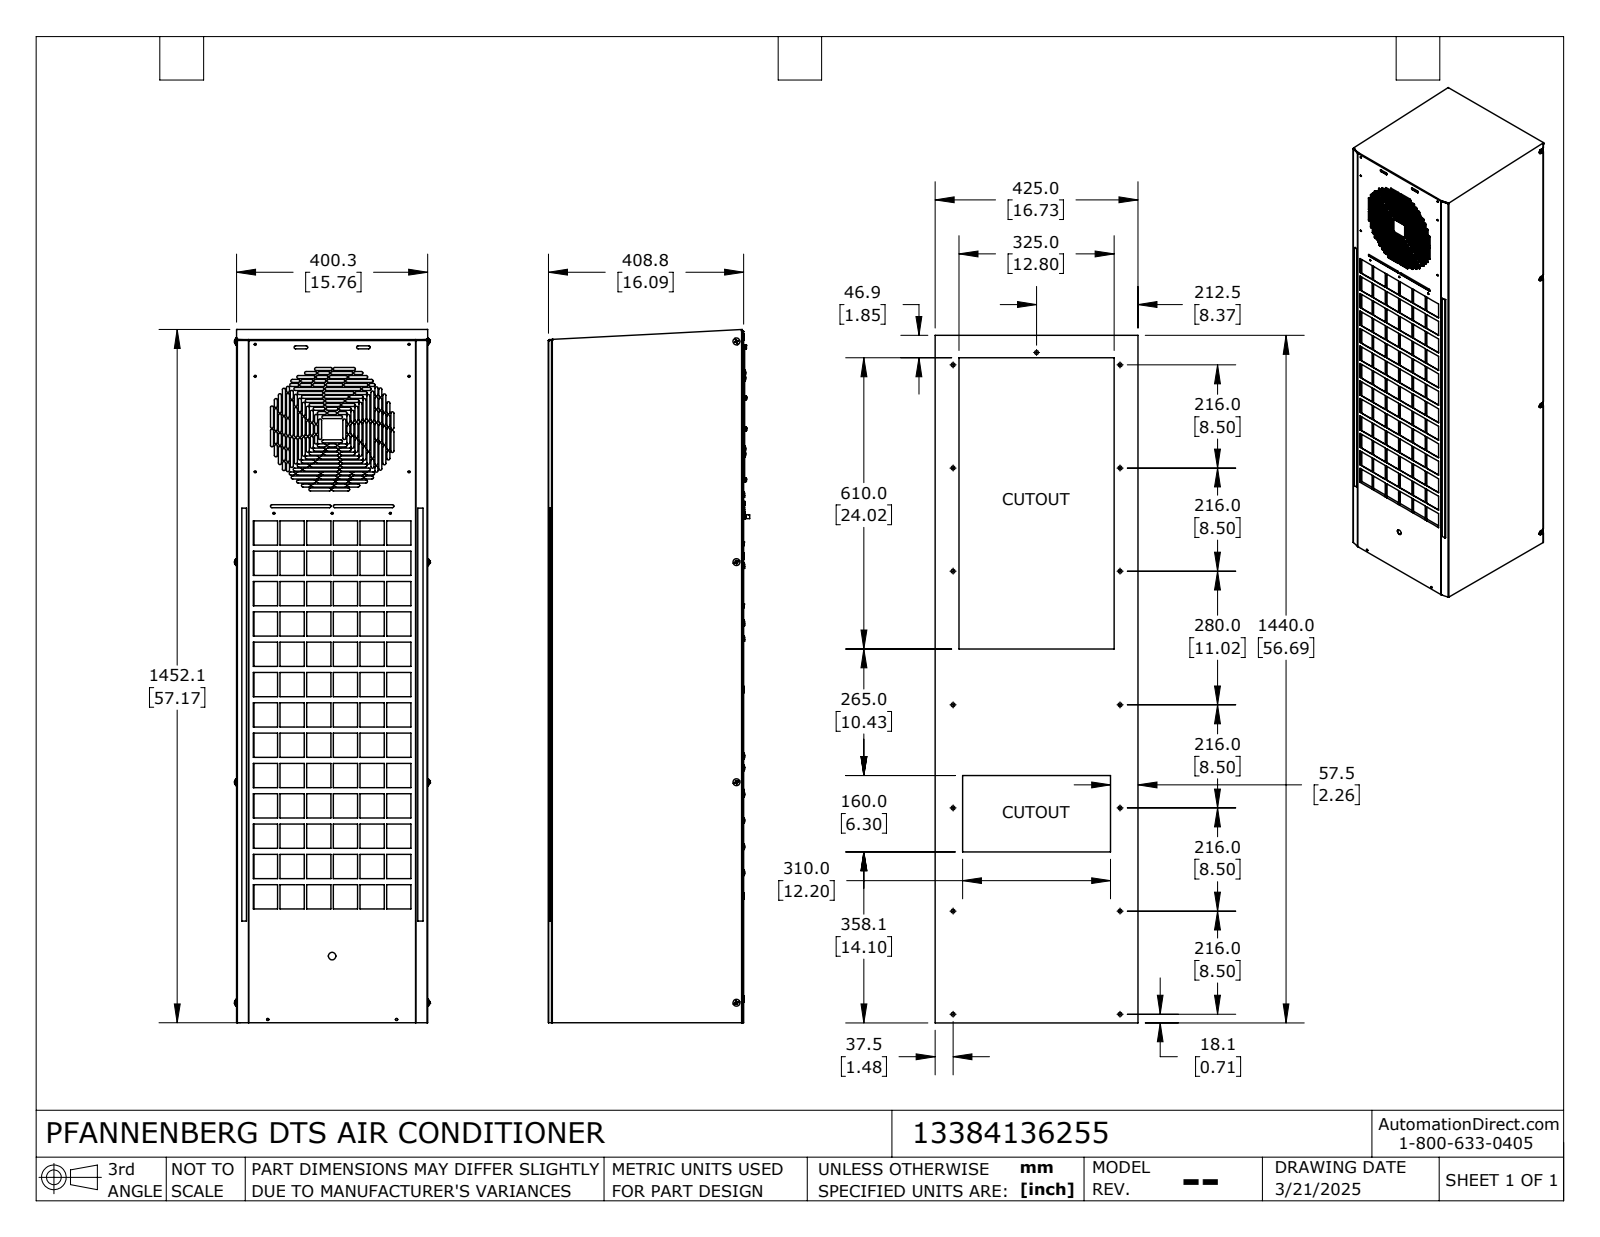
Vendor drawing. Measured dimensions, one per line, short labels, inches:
name: 13384136255_Default
written by: SolidWorks 2024 (CONFIG_CONTROL_DESIGN)
unit: in
bodies: 1 solid, 5369 faces (3016 planar, 1488 cylindrical, 865 other)
size: 57.171 × 16.603 × 16.113
volume: 13 807 in³; area: 6 261 in²
holes: 35× ⌀0.107, 27× ⌀0.165, 15× ⌀0.283, 14× ⌀0.189, 4× ⌀0.098, 4× ⌀0.161, 2× ⌀0.125, 2× ⌀0.276, 2× ⌀0.945, 1× ⌀0.122, 1× ⌀0.625, 1× ⌀0.731
bosses: 22× ⌀0.178, 15× ⌀0.512, 12× ⌀0.315, 12× ⌀0.157, 12× ⌀0.122, 6× ⌀0.354, 5× ⌀0.079, 4× ⌀0.573
rounds: 352× R0.125, 23× R0.031, 15× R0.198, 13× R0.087, 9× R0.076, 6× R0.132, 5× R0.118, 4× R0.016
face distances: 15.759, 0.143, 0.045, 15.815, 15.672, 16.096, 15.953, 0.281, 0.236, 16.051
hole spacings: 3.028, 0.022, 4.331, 1.507, 3.006, 3.05, 3.15, 4.724
